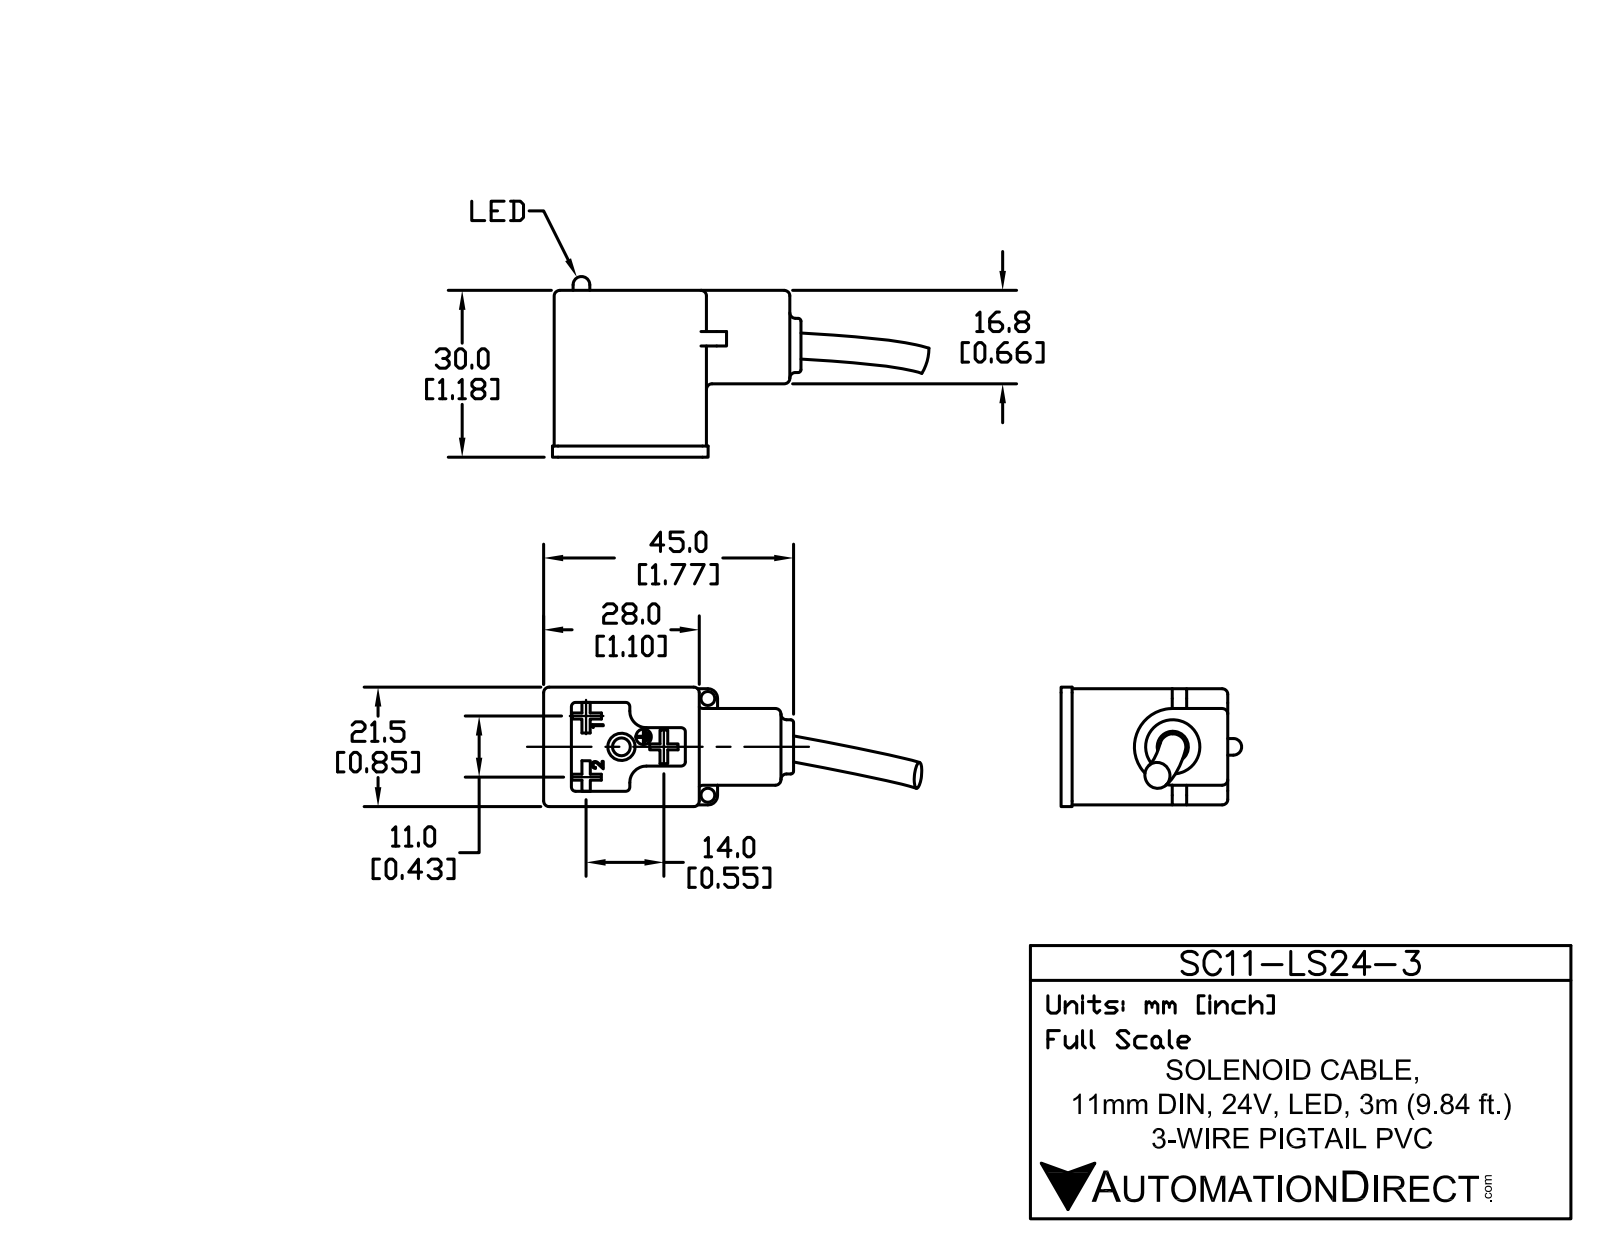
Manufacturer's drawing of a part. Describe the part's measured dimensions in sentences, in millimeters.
The part is named "SC11-LS24-3". Its 3-D file was written by "SolidWorks 2011 (AUTOMOTIVE_DESIGN)". It is 3 solids with 205 faces: 131 planar, 46 cylindrical and 28 other. Overall it measures 67.77 by 36.8 by 21.5 millimeters. Its volume is 20 000 cubic millimeters and its surface area 6 766 square millimeters. Round holes: 2 of diameter 2.5, 1 of diameter 2.78, 1 of diameter 3.2, 1 of diameter 4.9, 1 of diameter 5.6, 1 of diameter 6.6. Round bosses or shafts: 1 of diameter 9.75, 1 of diameter 6.5, 1 of diameter 3, 1 of diameter 2.75. Partial cylindrical surfaces (rounded edges, fillets, slot ends): 19 of radius 1, 6 of radius 0.75, 2 of radius 1.75, 2 of radius 3, 1 of radius 6.9. The main face-to-face distances are 20.9, 30, 27.4, 28, 2, 3.55, 17.35, 27.95, 29.95, 13.8. The hole center spacings are 14.21, 17.82, 4.32, 17.4.
